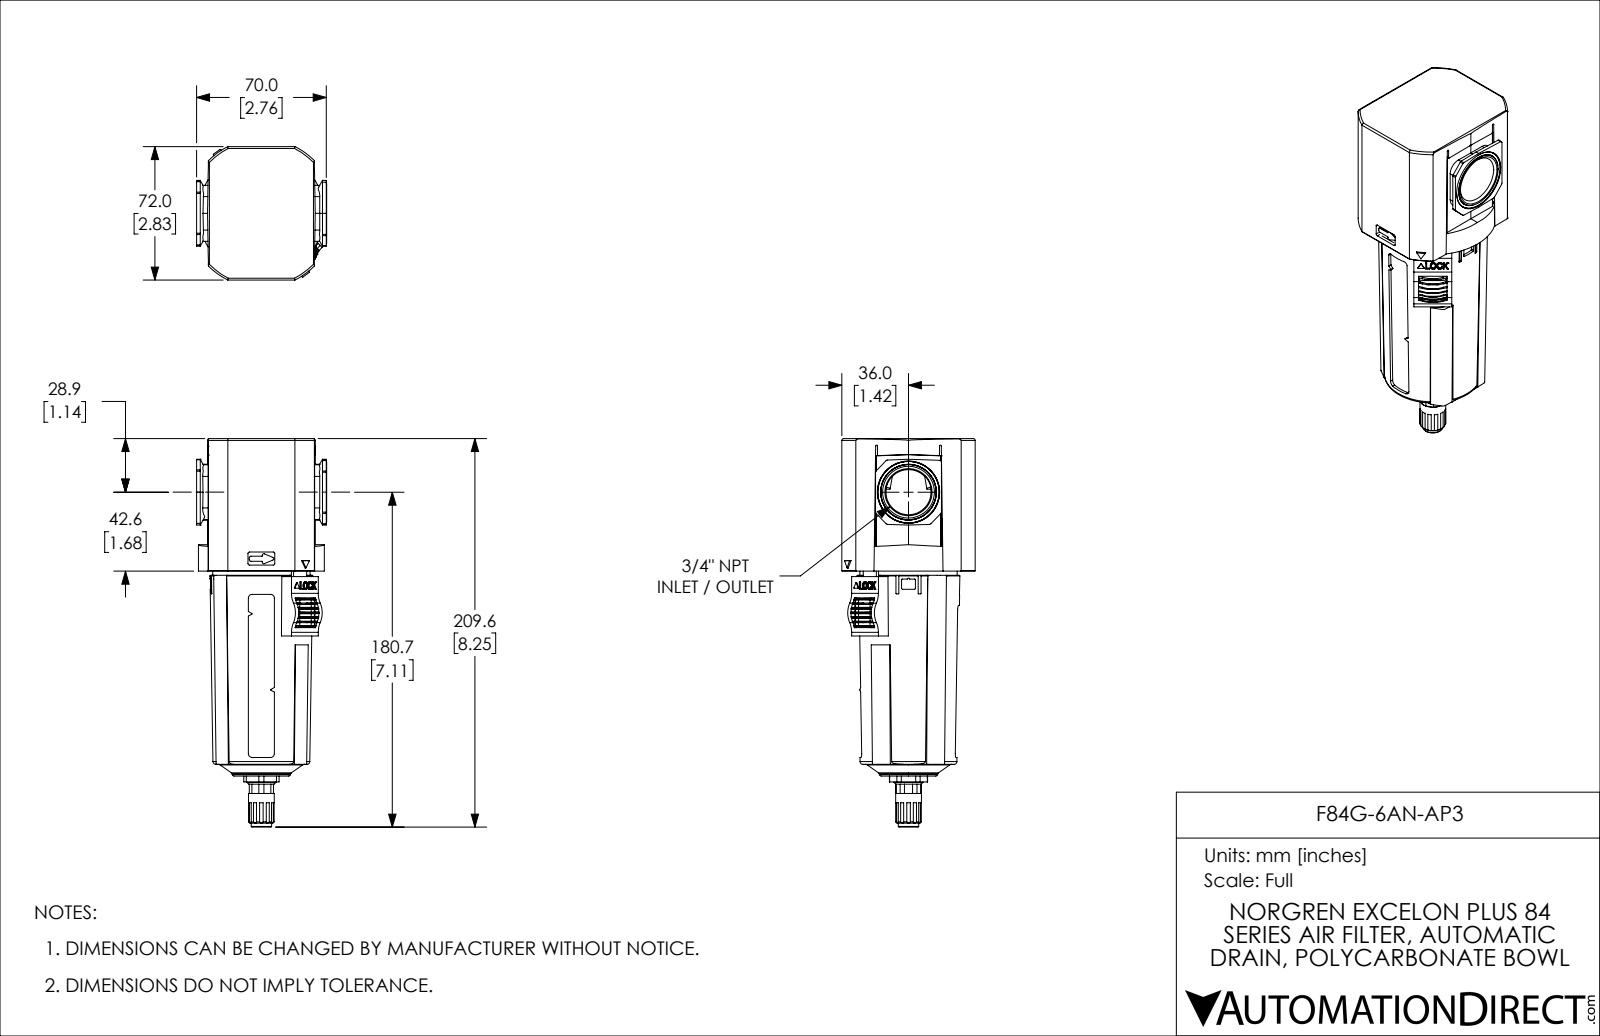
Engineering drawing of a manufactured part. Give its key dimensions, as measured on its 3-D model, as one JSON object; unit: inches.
{"part_name": "F84G-6AN-AP3", "step_written_by": "SolidWorks 2021 (CONFIG_CONTROL_DESIGN)", "units": "inches", "bodies": {"solids": 5, "faces": 1089, "planar": 504, "cylindrical": 405, "other": 180}, "overall_size": [8.251, 2.835, 2.766], "volume_in3": 27.45, "surface_area_in2": 150.4, "round_holes": [[0.163, 2], [0.22, 1], [0.246, 1], [0.776, 1], [0.969, 1], [2.461, 1]], "round_bosses_or_shafts": [[0.315, 2], [0.276, 2], [1, 1], [0.969, 1], [0.907, 1], [0.617, 1], [0.547, 1], [0.433, 1]], "partial_cylinders_radius": [[0.039, 44], [0.02, 40], [0.01, 24], [0.028, 16], [0.008, 10], [0.038, 8], [0.045, 8], [0.06, 8]], "face_to_face_distances": [0.059, 2.411, 2.352, 2.835, 0.035, 2.317, 2.376, 2.756, 0.404, 0.439], "hole_center_spacings": [0.594, 1.189]}
